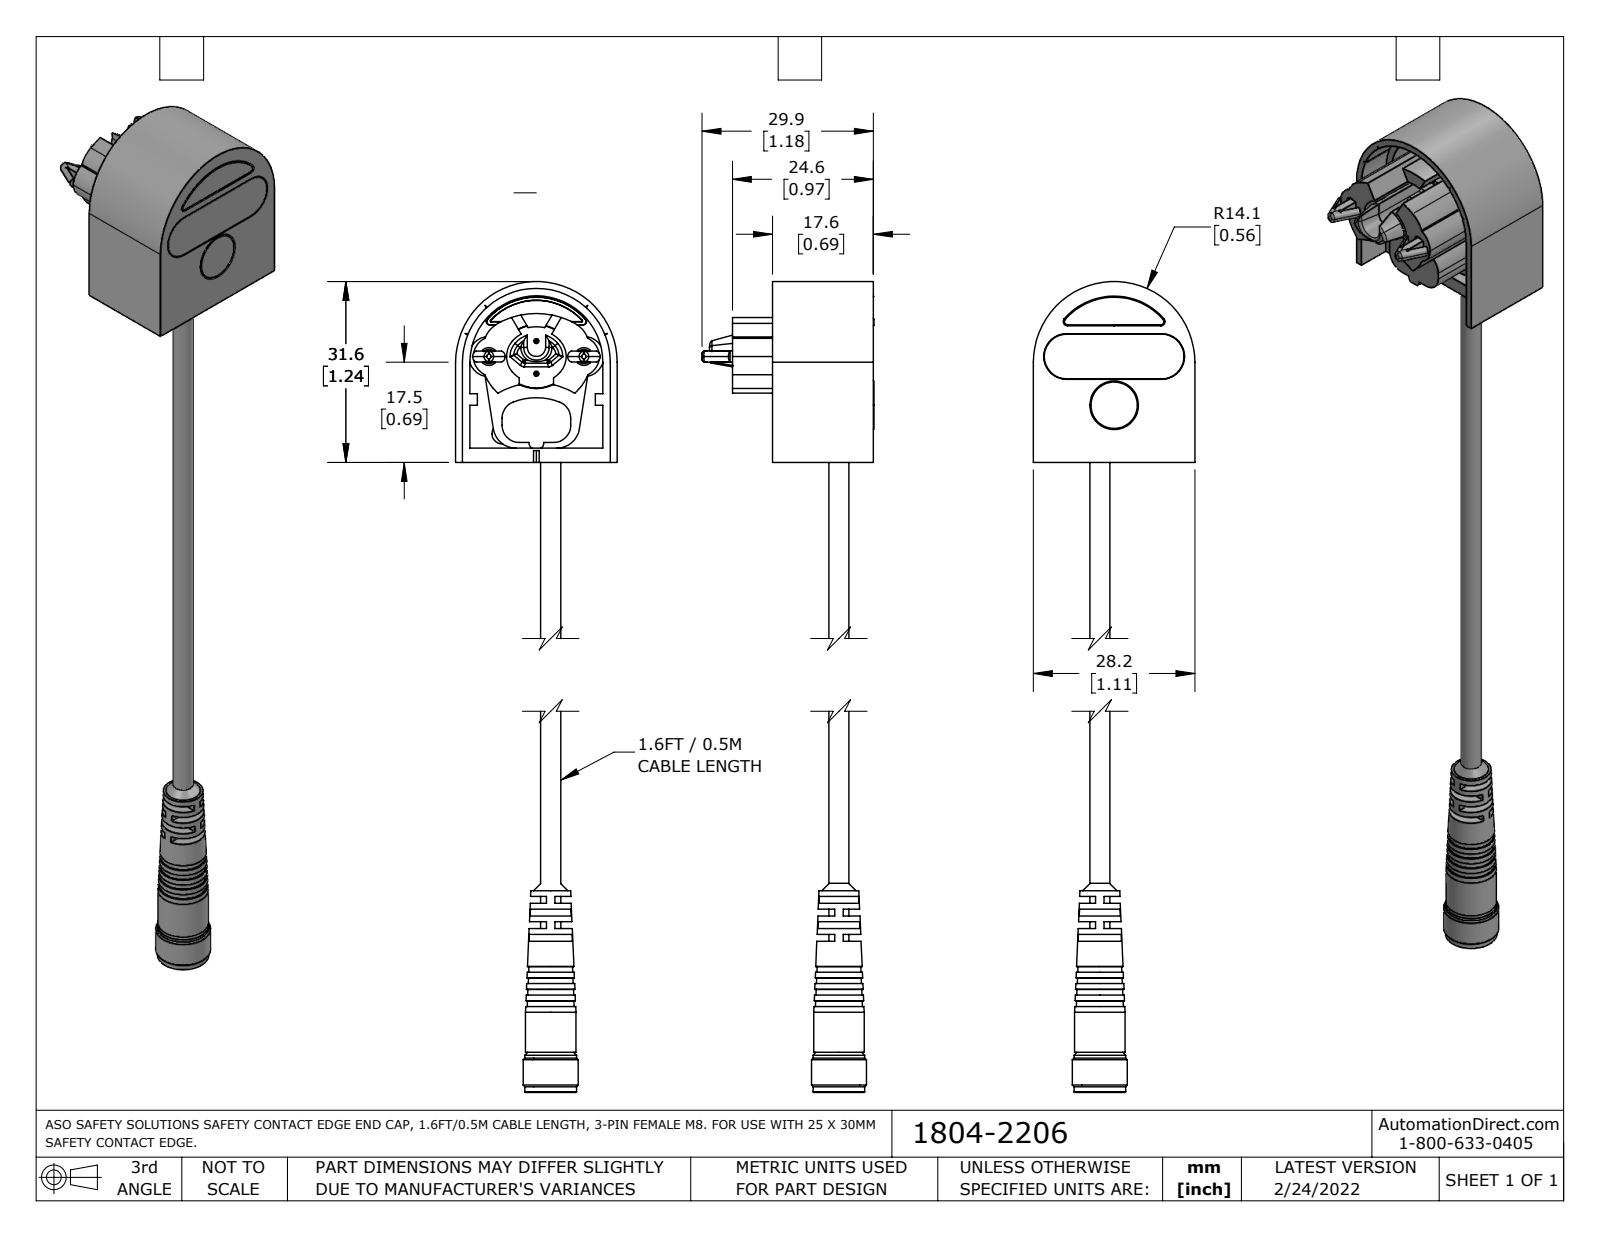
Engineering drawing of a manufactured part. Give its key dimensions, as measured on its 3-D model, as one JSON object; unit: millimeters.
{"part_name": "1804-2206_Default", "step_written_by": "SolidWorks 2021 (CONFIG_CONTROL_DESIGN)", "units": "millimeters", "bodies": {"solids": 11, "faces": 689, "planar": 231, "cylindrical": 286, "other": 172}, "overall_size": [172.5, 30, 28.2], "volume_mm3": 12626, "surface_area_mm2": 14201, "round_holes": [[0.5, 4], [0.8, 3], [0.85, 3], [1.6, 3], [3.5, 3], [3.1, 2], [4, 2], [5.5, 2], [3.4, 1], [5.9, 1], [6.9, 1], [7.2, 1]], "round_bosses_or_shafts": [[1.2, 13], [0.5, 6], [3.5, 3], [1, 3], [5, 2], [2.5, 2], [2, 2], [1.66, 2]], "partial_cylinders_radius": [[1, 12], [0.1, 9], [0.3, 6], [3, 6], [3.5, 6], [0.5, 5], [4, 4], [5, 4]], "face_to_face_distances": [2.5, 1.8, 1, 1.2, 28.2, 0.8, 1.3, 2, 25.7, 7.8], "hole_center_spacings": [1.4, 1.75, 16.6, 2.47, 8.73, 8.83, 22.14, 22.66]}
